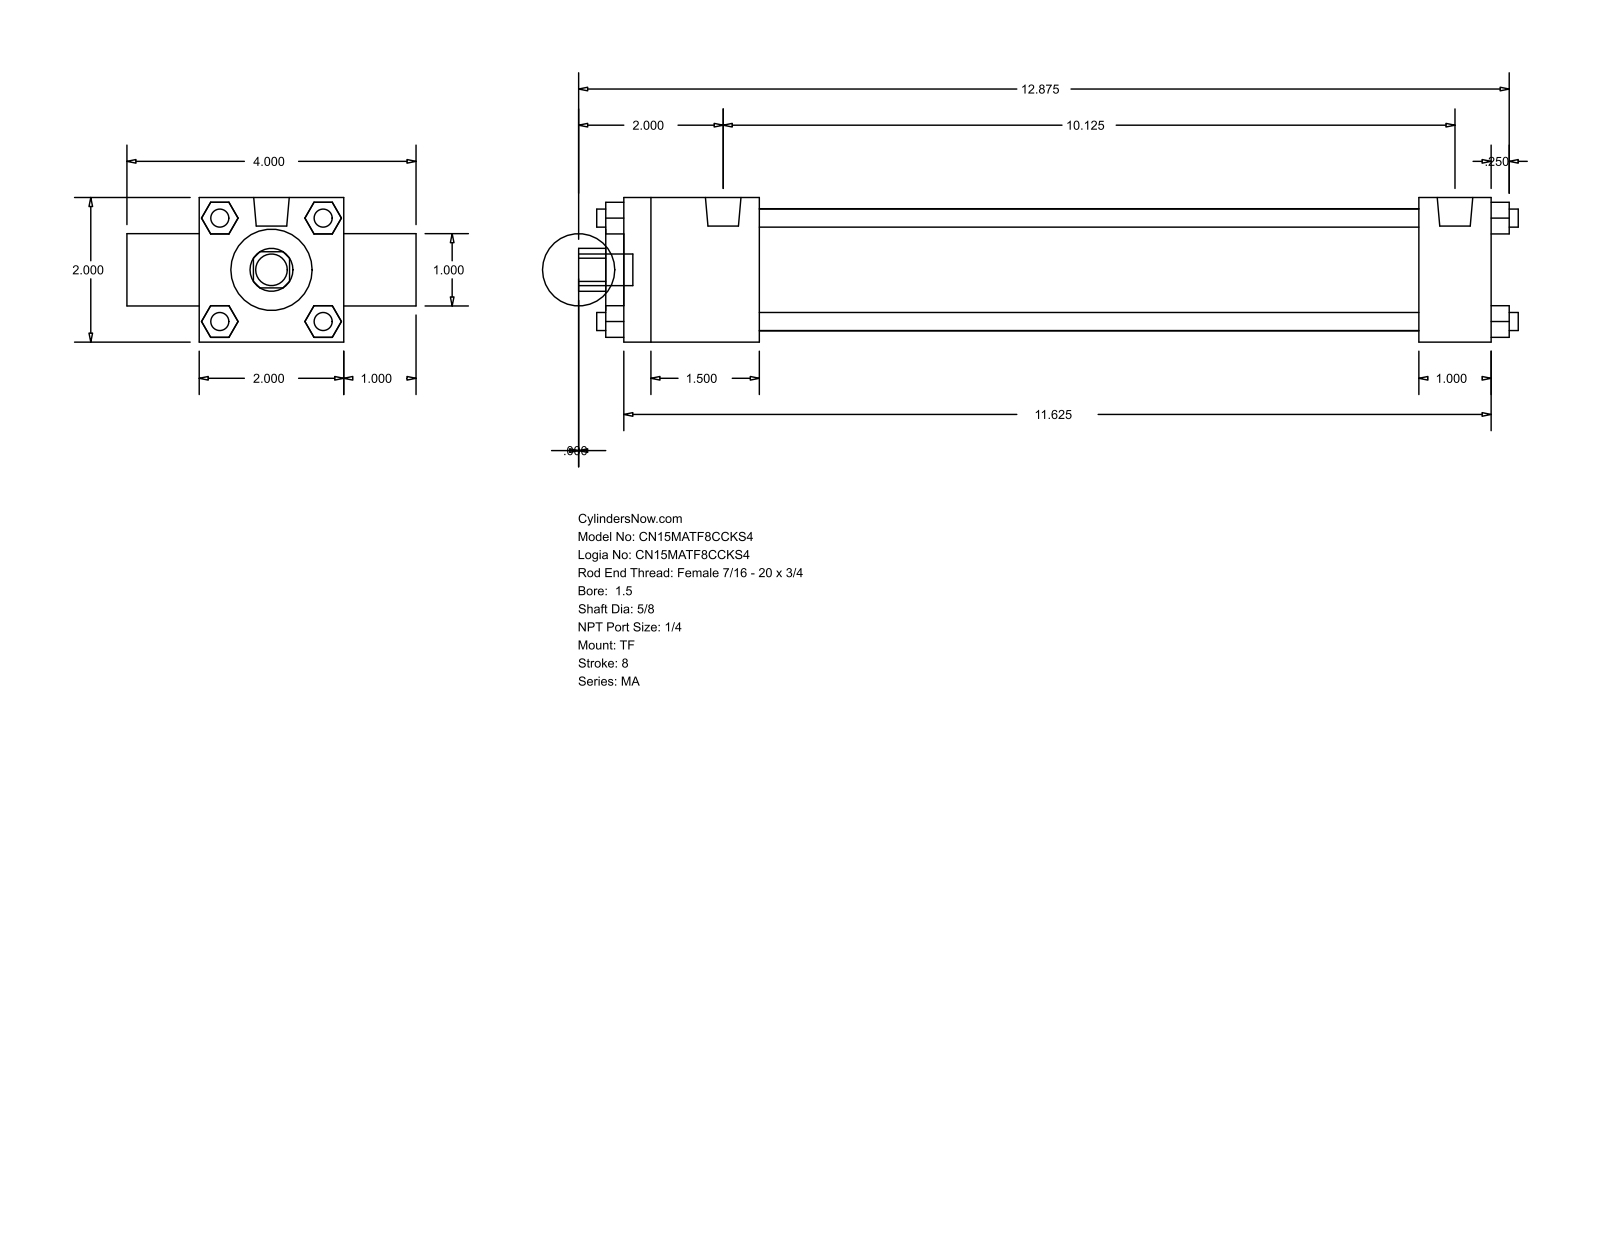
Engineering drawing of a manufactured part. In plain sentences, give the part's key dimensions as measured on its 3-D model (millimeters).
The part is named "MA_TF__0150_0.625". Its 3-D file was written by "GSSL Pune (CONFIG_CONTROL_DESIGN)". It is 0 solids with 120 faces: 92 planar, 28 cylindrical and 0 other. Overall it measures 330.2 by 101.6 by 50.8 millimeters. Round holes: 1 of diameter 15.88, 1 of diameter 25.4, 1 of diameter 28.57, 1 of diameter 42.93. Round bosses or shafts: 4 of diameter 6.35, 3 of diameter 7.94, 2 of diameter 12.49, 1 of diameter 11.11. Partial cylindrical surfaces (rounded edges, fillets, slot ends): 1 of radius 7.54. The main face-to-face distances are 50.8, 304.8, 25.4, 76.2, 47.62, 279.39, 231.77, 257.18, 25.41, 311.15.
